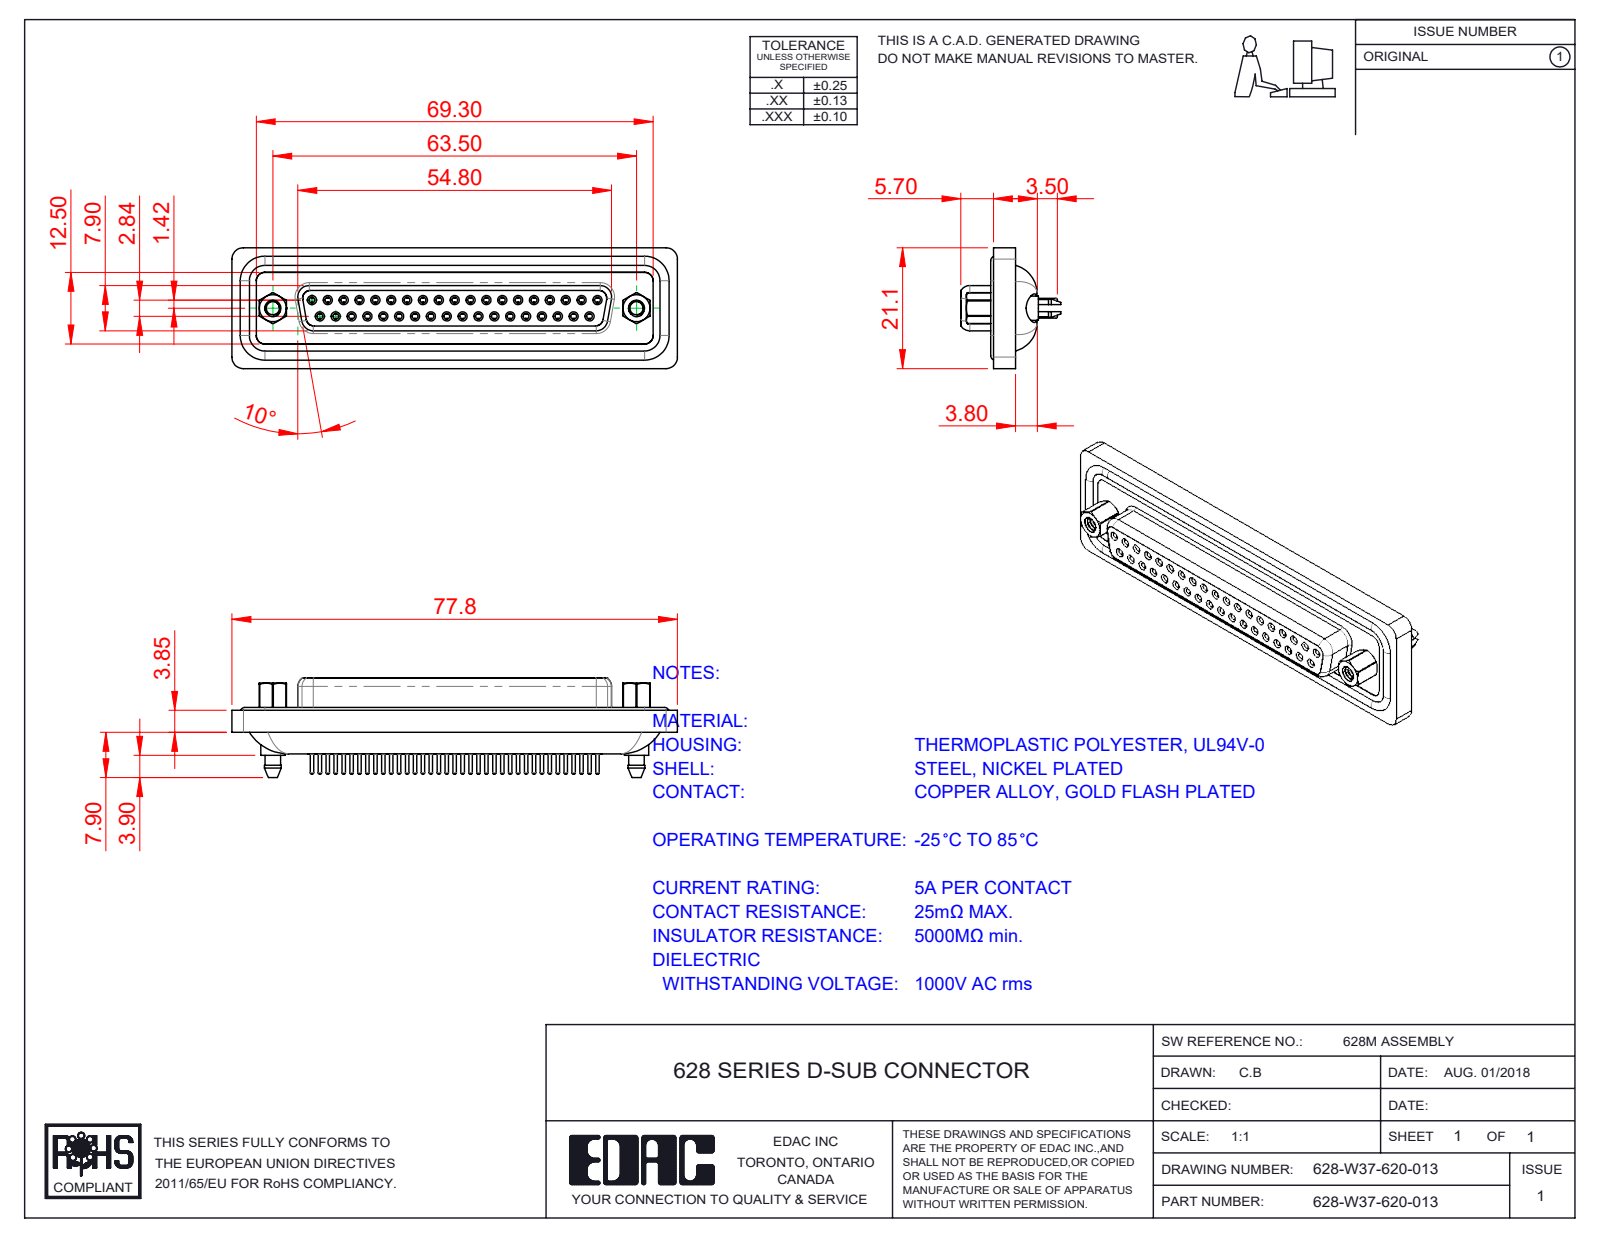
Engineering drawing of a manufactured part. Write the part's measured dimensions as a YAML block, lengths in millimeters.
part_name: "628W Contact Row 2_20; 628-W37-620-013; 628W Housing_37 Contacts; 628W Contact Row 1_20 (+4 more)"
step_written_by: "SolidWorks 2020 (CONFIG_CONTROL_DESIGN)"
units: millimeters
bodies: {solids: 45, faces: 2580, planar: 670, cylindrical: 1029, other: 881}
overall_size: [77.8, 21.1, 17.45]
volume: 11033
surface_area: 18127
round_holes:
  - {diameter: 1, count: 37}
  - {diameter: 1.1, count: 37}
  - {diameter: 1.5, count: 37}
  - {diameter: 1.7, count: 37}
  - {diameter: 1.8, count: 37}
  - {diameter: 2, count: 37}
  - {diameter: 2.26, count: 2}
  - {diameter: 2.29, count: 2}
  - {diameter: 4, count: 2}
  - {diameter: 4.8, count: 2}
  - {diameter: 5, count: 2}
round_bosses_or_shafts:
  - {diameter: 1.6, count: 41}
  - {diameter: 2.2, count: 37}
  - {diameter: 0.6, count: 37}
  - {diameter: 1.5, count: 8}
  - {diameter: 5.4, count: 2}
  - {diameter: 4.9, count: 2}
  - {diameter: 4.25, count: 2}
  - {diameter: 2.79, count: 2}
partial_cylinders:
  - {radius: 1.5, count: 16}
  - {radius: 2, count: 16}
  - {radius: 1.35, count: 8}
  - {radius: 1.6, count: 6}
  - {radius: 0.5, count: 4}
  - {radius: 0.9, count: 4}
  - {radius: 1.75, count: 4}
  - {radius: 2.7, count: 4}
face_to_face_distances: [0.4, 7.45, 7.5, 8.45, 6.2, 13.65, 3.75, 4.1, 5.65, 1.1]
hole_center_spacings: [3.16, 2.77, 5.54, 8.31, 5.04, 7.49, 11.08, 13.85]
